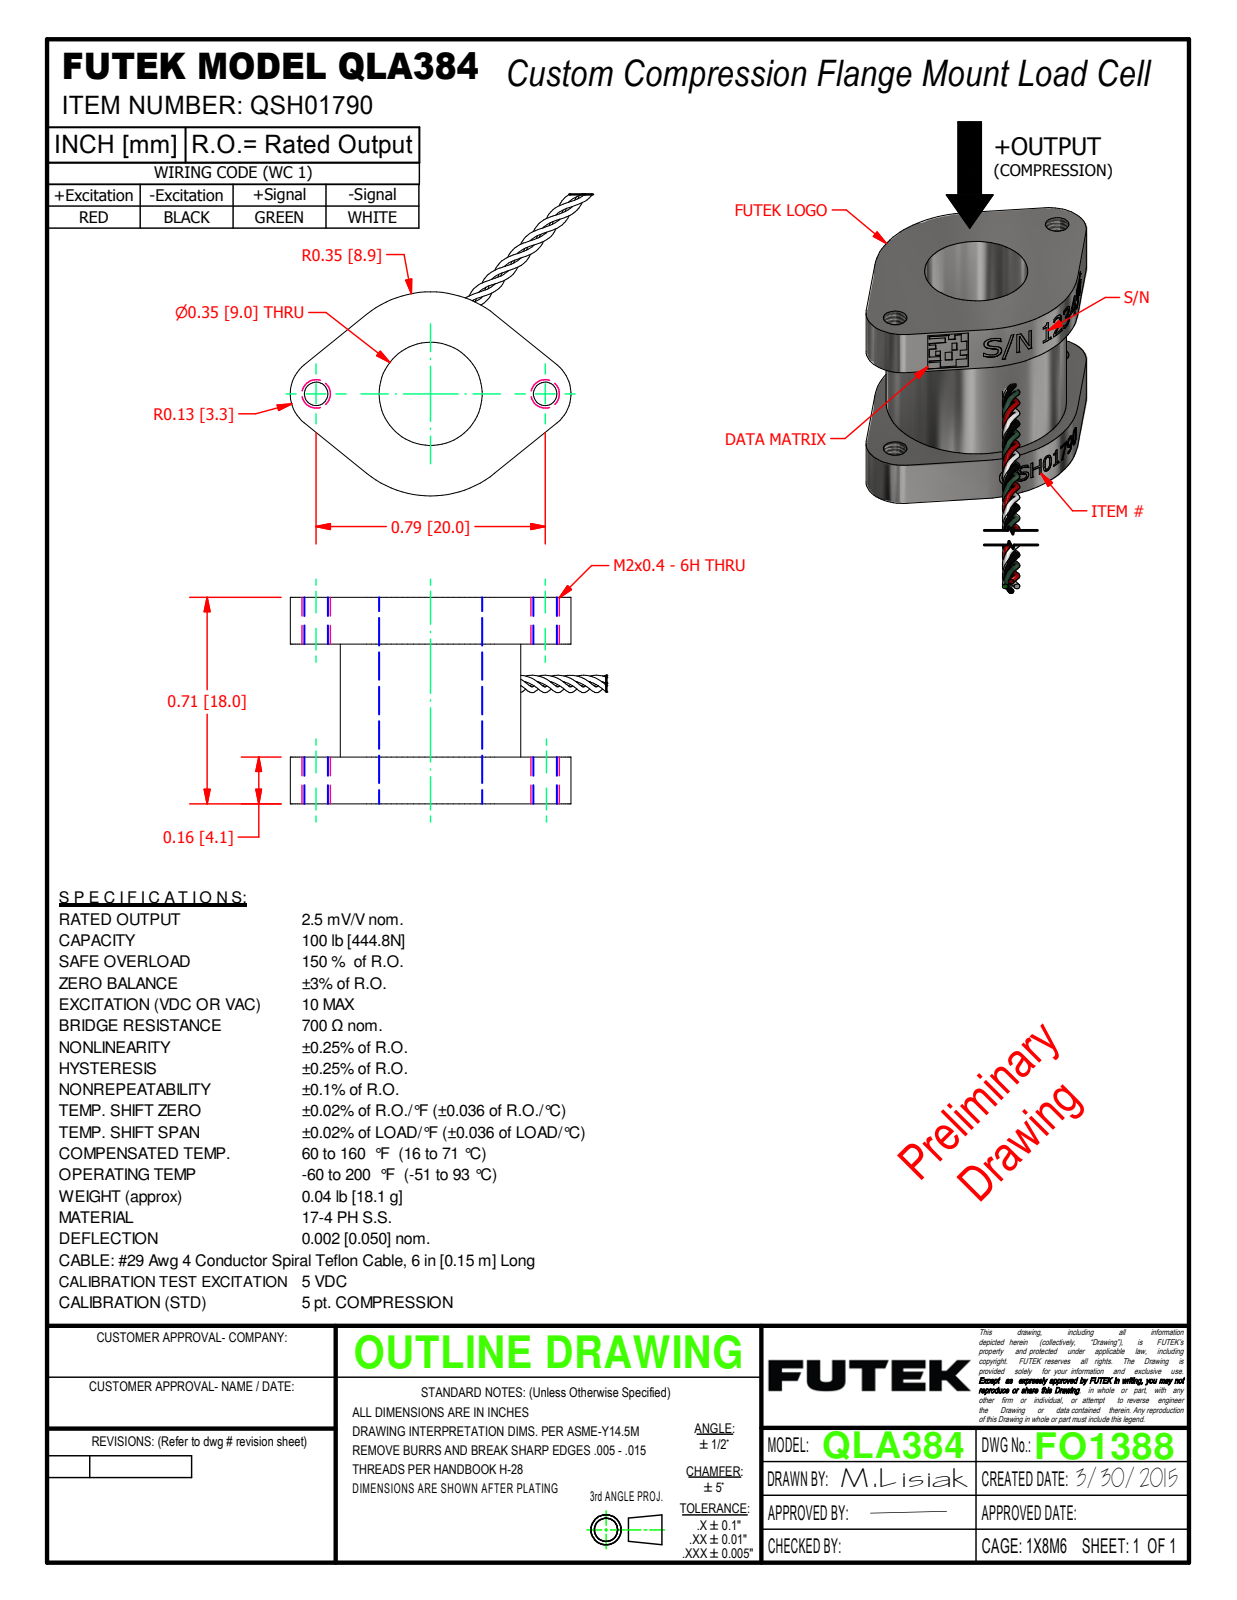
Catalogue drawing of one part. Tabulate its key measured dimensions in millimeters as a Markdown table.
| quantity | value |
| --- | --- |
| part name | FO1388; Cable 29 Awg Approximation |
| STEP written by | Autodesk Inventor 2018 (AUTOMOTIVE_DESIGN) |
| units | millimeters |
| bodies | 5 solids, 380 faces (181 planar, 38 cylindrical, 161 other) |
| overall size | 50.7 × 49.7 × 18 |
| volume | 3 180 mm³ |
| surface area | 2 610 mm² |
| round holes (diameter × count) | 2.1 × 2, 9 × 1 |
| round bosses / shafts (diameter × count) | 15.7 × 1 |
| partial cylindrical surfaces (radius × count) | 3.3 × 2, 8.9 × 1, 8.9 × 1 |
| main face-to-face distances | 18, 4.1, 13.9, 17.8, 9.9, 17.8, 50.8, 3.6, 3.8, 3.4 |
| hole center spacings | 10, 20 |
